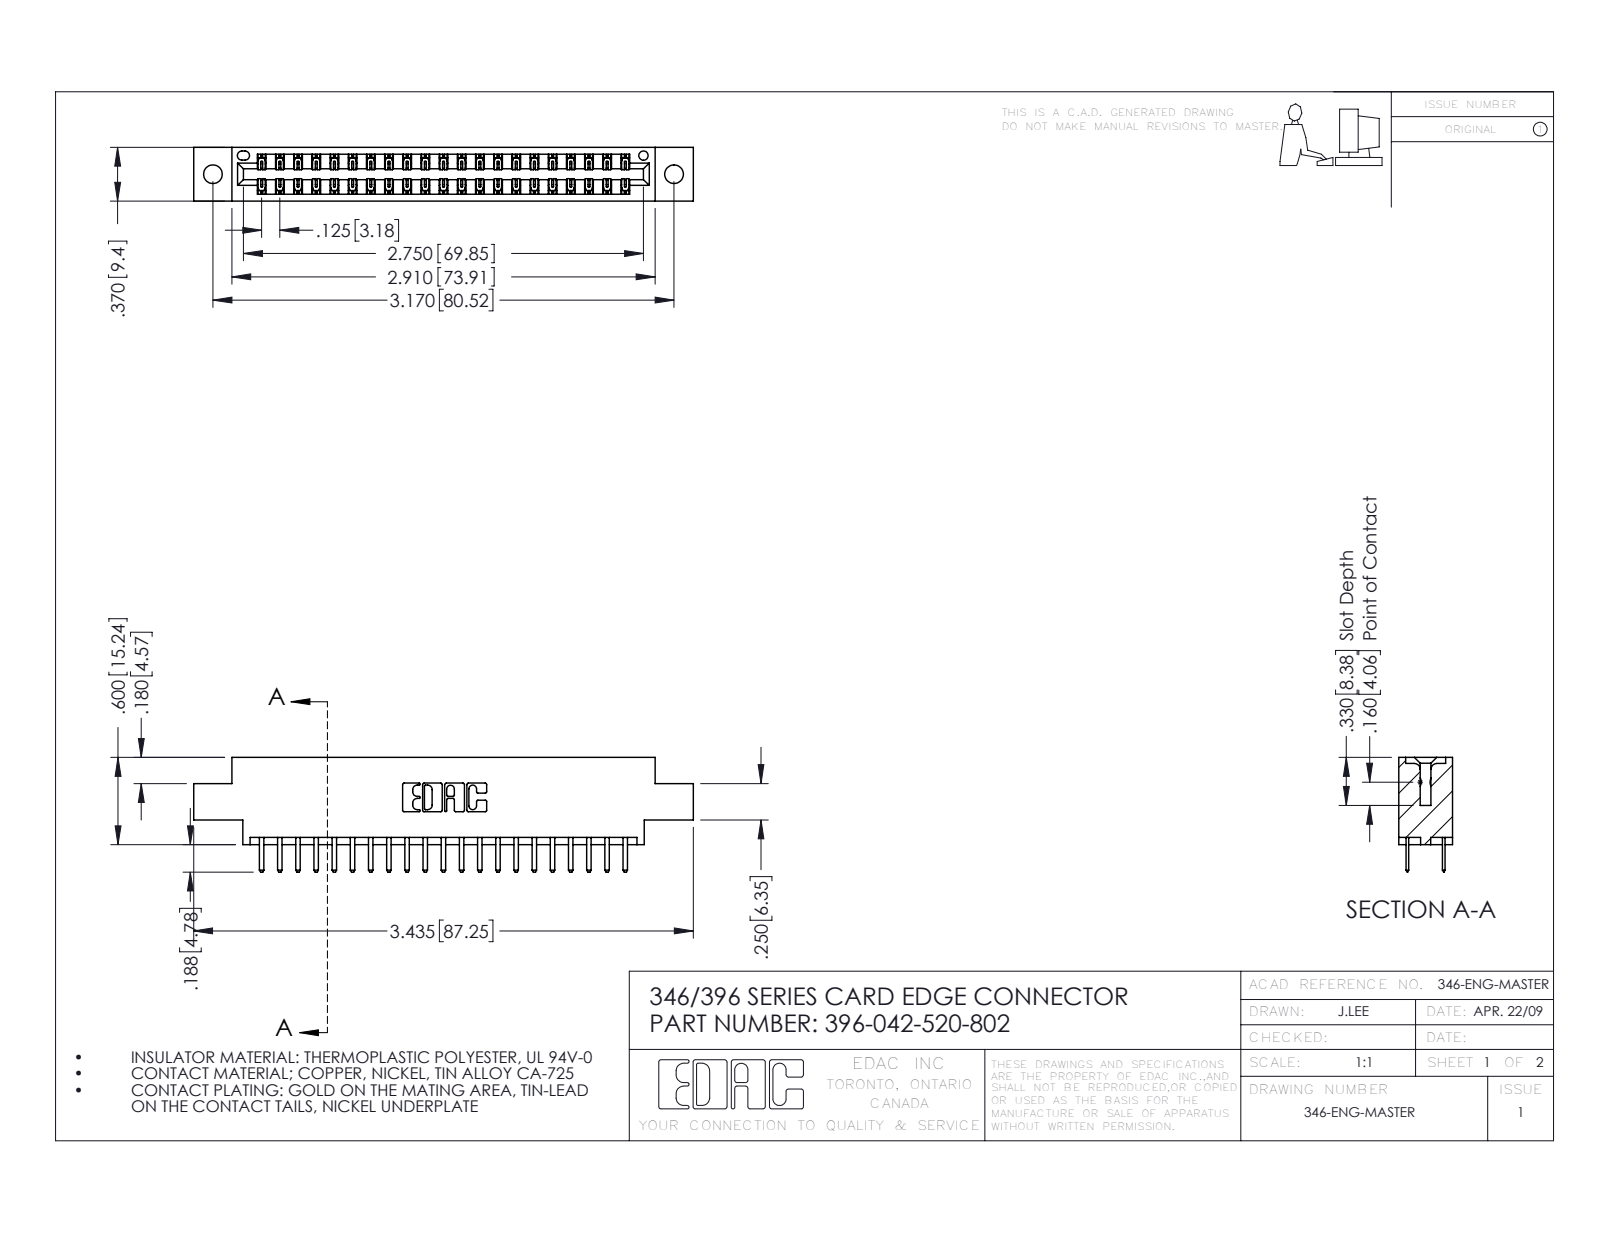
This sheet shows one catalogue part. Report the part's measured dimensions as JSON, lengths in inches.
{"part_name": "346 Part_0.170 Offset - 0.128 Dia; 396-042-520-802; 345-292-001_345-293-120", "step_written_by": "SolidWorks 2016 (CONFIG_CONTROL_DESIGN)", "units": "inches", "bodies": {"solids": 43, "faces": 2478, "planar": 1634, "cylindrical": 844, "other": 0}, "overall_size": [3.435, 0.788, 0.37], "volume_in3": 0.496, "surface_area_in2": 16.61, "round_holes": [[0.128, 2], [0.064, 1]], "partial_cylinders_radius": [[0.006, 63], [0.01, 46], [0.01, 22], [0.007, 6], [0.031, 6], [0.026, 3], [0.014, 2], [0.022, 2]], "face_to_face_distances": [0.048, 0.322, 0.25, 0.37, 0.275, 0.072, 0.298, 0.025, 0.148, 0.222], "hole_center_spacings": [0.246, 2.963, 3.17]}
